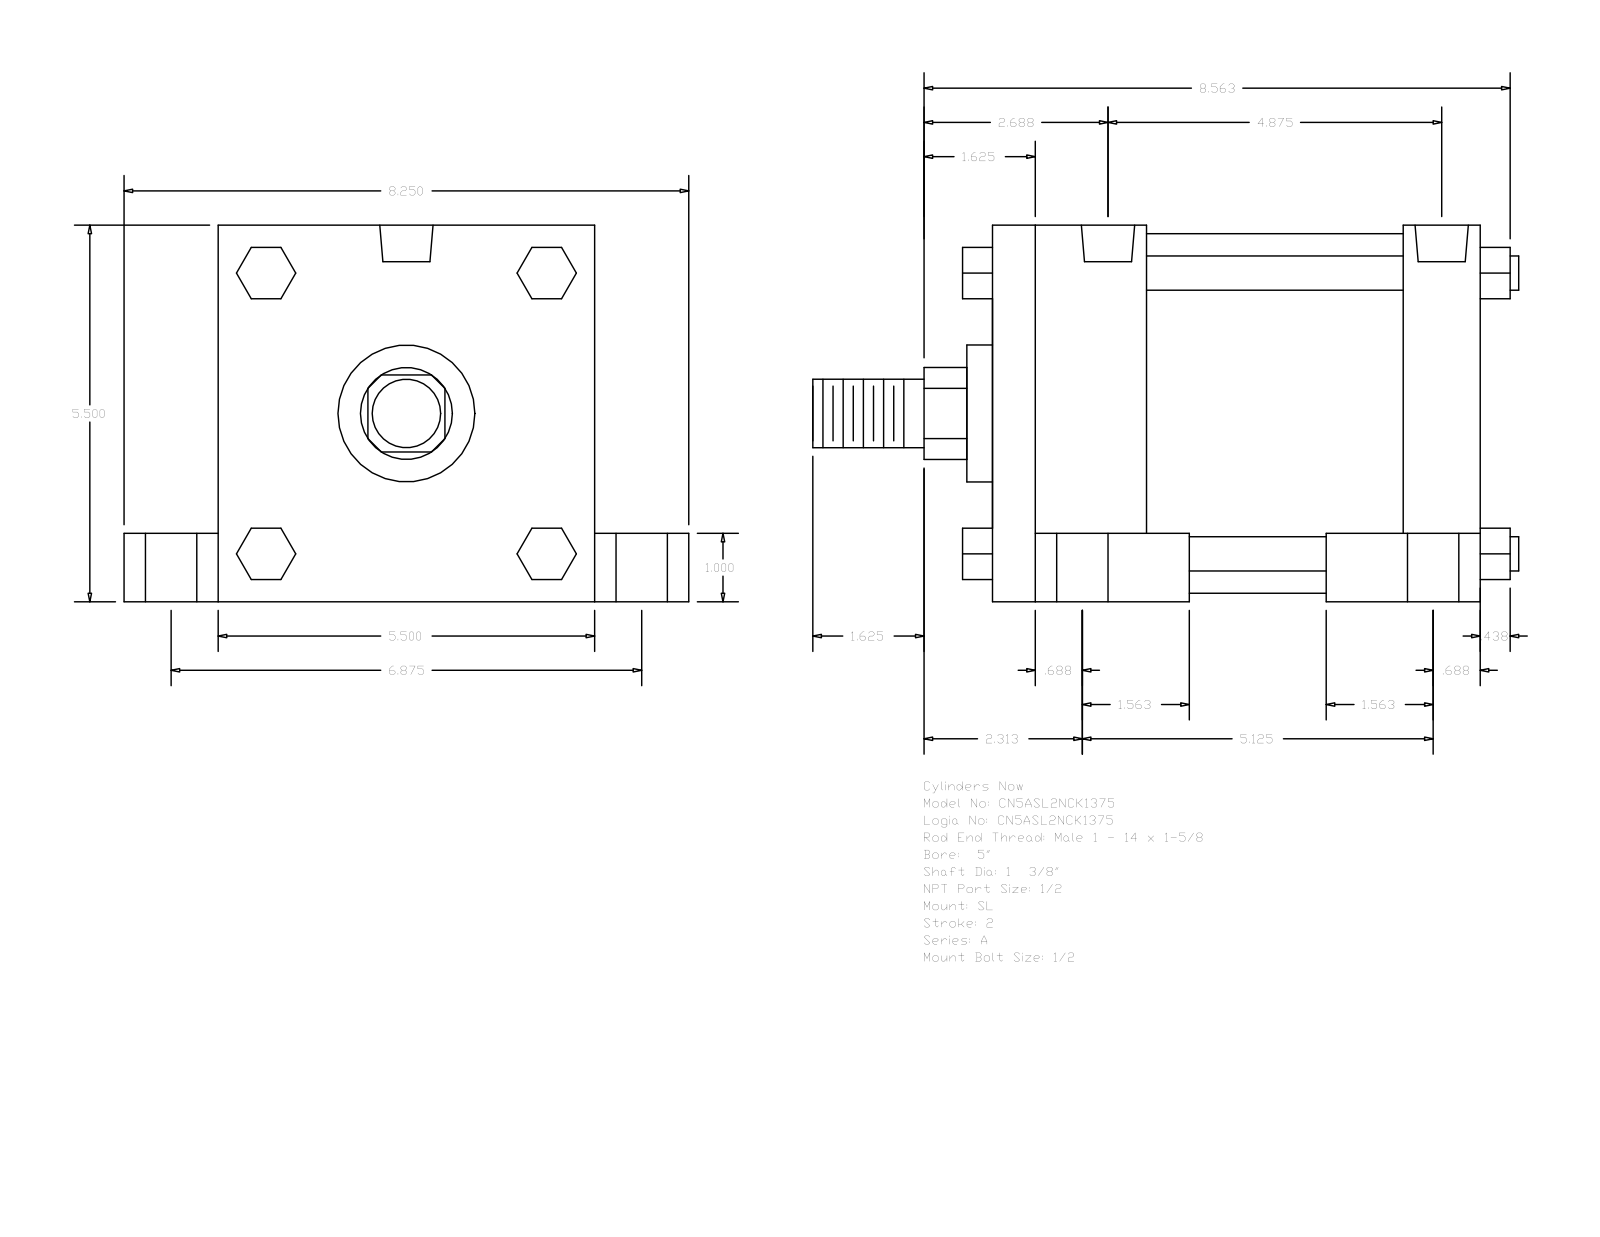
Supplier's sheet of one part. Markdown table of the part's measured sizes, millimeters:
| quantity | value |
| --- | --- |
| part name | A_SL__0500_1.375 |
| STEP written by | GSSL Pune (CONFIG_CONTROL_DESIGN) |
| units | millimeters |
| bodies | 0 solids, 150 faces (114 planar, 36 cylindrical, 0 other) |
| overall size | 261.94 × 209.55 × 139.7 |
| round holes (diameter × count) | 8.73 × 4, 19.05 × 4, 25.4 × 4, 19.77 × 2 |
| round bosses / shafts (diameter × count) | 12.7 × 4, 133.35 × 1, 50.8 × 1, 34.92 × 1, 25.4 × 1 |
| partial cylindrical surfaces (radius × count) | 17.06 × 1 |
| main face-to-face distances | 139.7, 180.98, 57.15, 28.58, 25.4, 114.3, 34.93, 174.63, 152.4, 95.25 |
| hole center spacings | 2.39, 87.31, 87.37, 87.83, 88.12, 119.05, 121.44, 130.17 |
